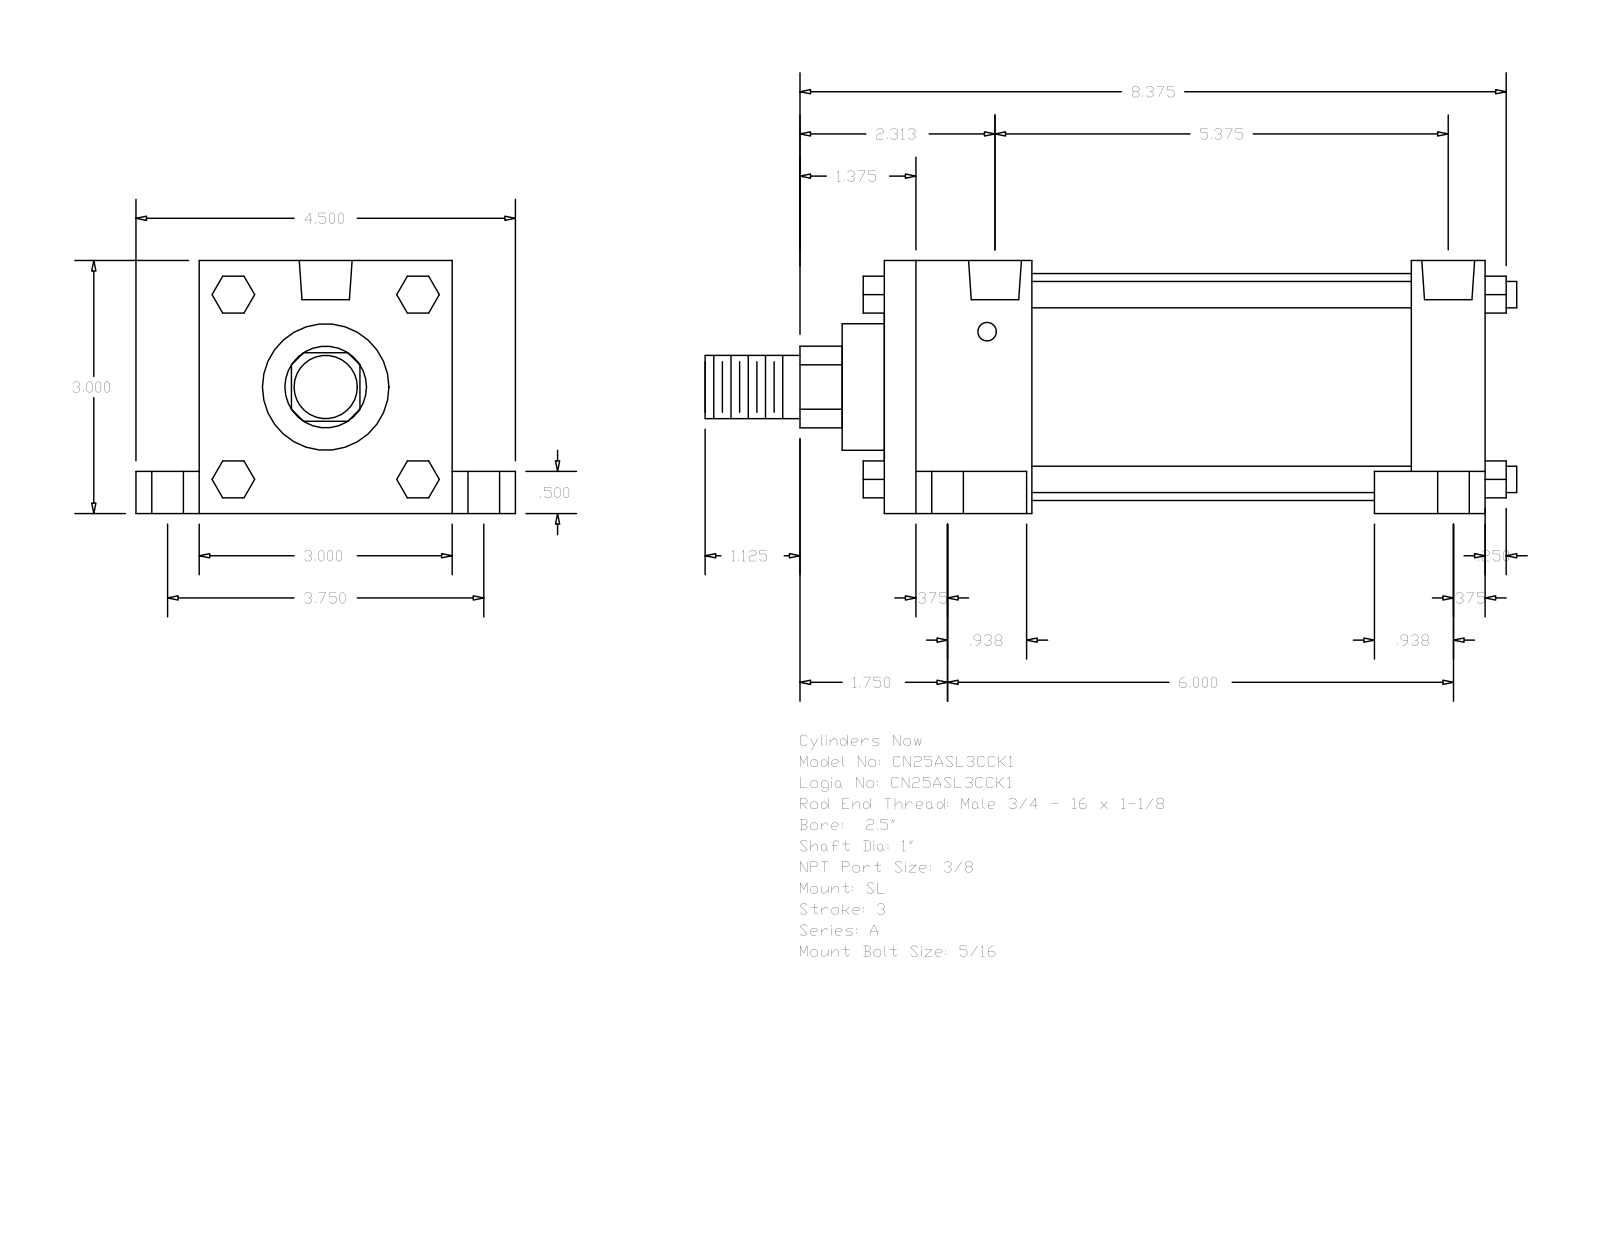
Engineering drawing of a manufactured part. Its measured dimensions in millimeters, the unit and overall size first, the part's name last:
Units: millimetres
Overall size (bounding box): 244.47 × 114.3 × 76.2
Round holes (diameter × count): ⌀5.56 ×4, ⌀9.53 ×4, ⌀15.88 ×4, ⌀15.93 ×2
Round bosses / shafts (diameter × count): ⌀7.94 ×4, ⌀68.33 ×1, ⌀38.1 ×1, ⌀25.4 ×1, ⌀19.05 ×1
Partial cylindrical surfaces — rounded edges, fillets, slot ends (radius × count): R12.29 ×1
Main face-to-face distances: 76.2, 180.98, 114.3, 12.7, 44.45, 136.53, 158.75, 22.23, 19.05, 63.5
Hole centre spacings: 2.38, 47.63, 47.65, 49.09, 49.72, 95.24, 138.9, 141.28
Bodies: 0 solids, 148 faces (112 planar, 36 cylindrical, 0 other)
Part name (STEP PRODUCT): A_SL__0250_1
STEP written by: GSSL Pune (CONFIG_CONTROL_DESIGN)
